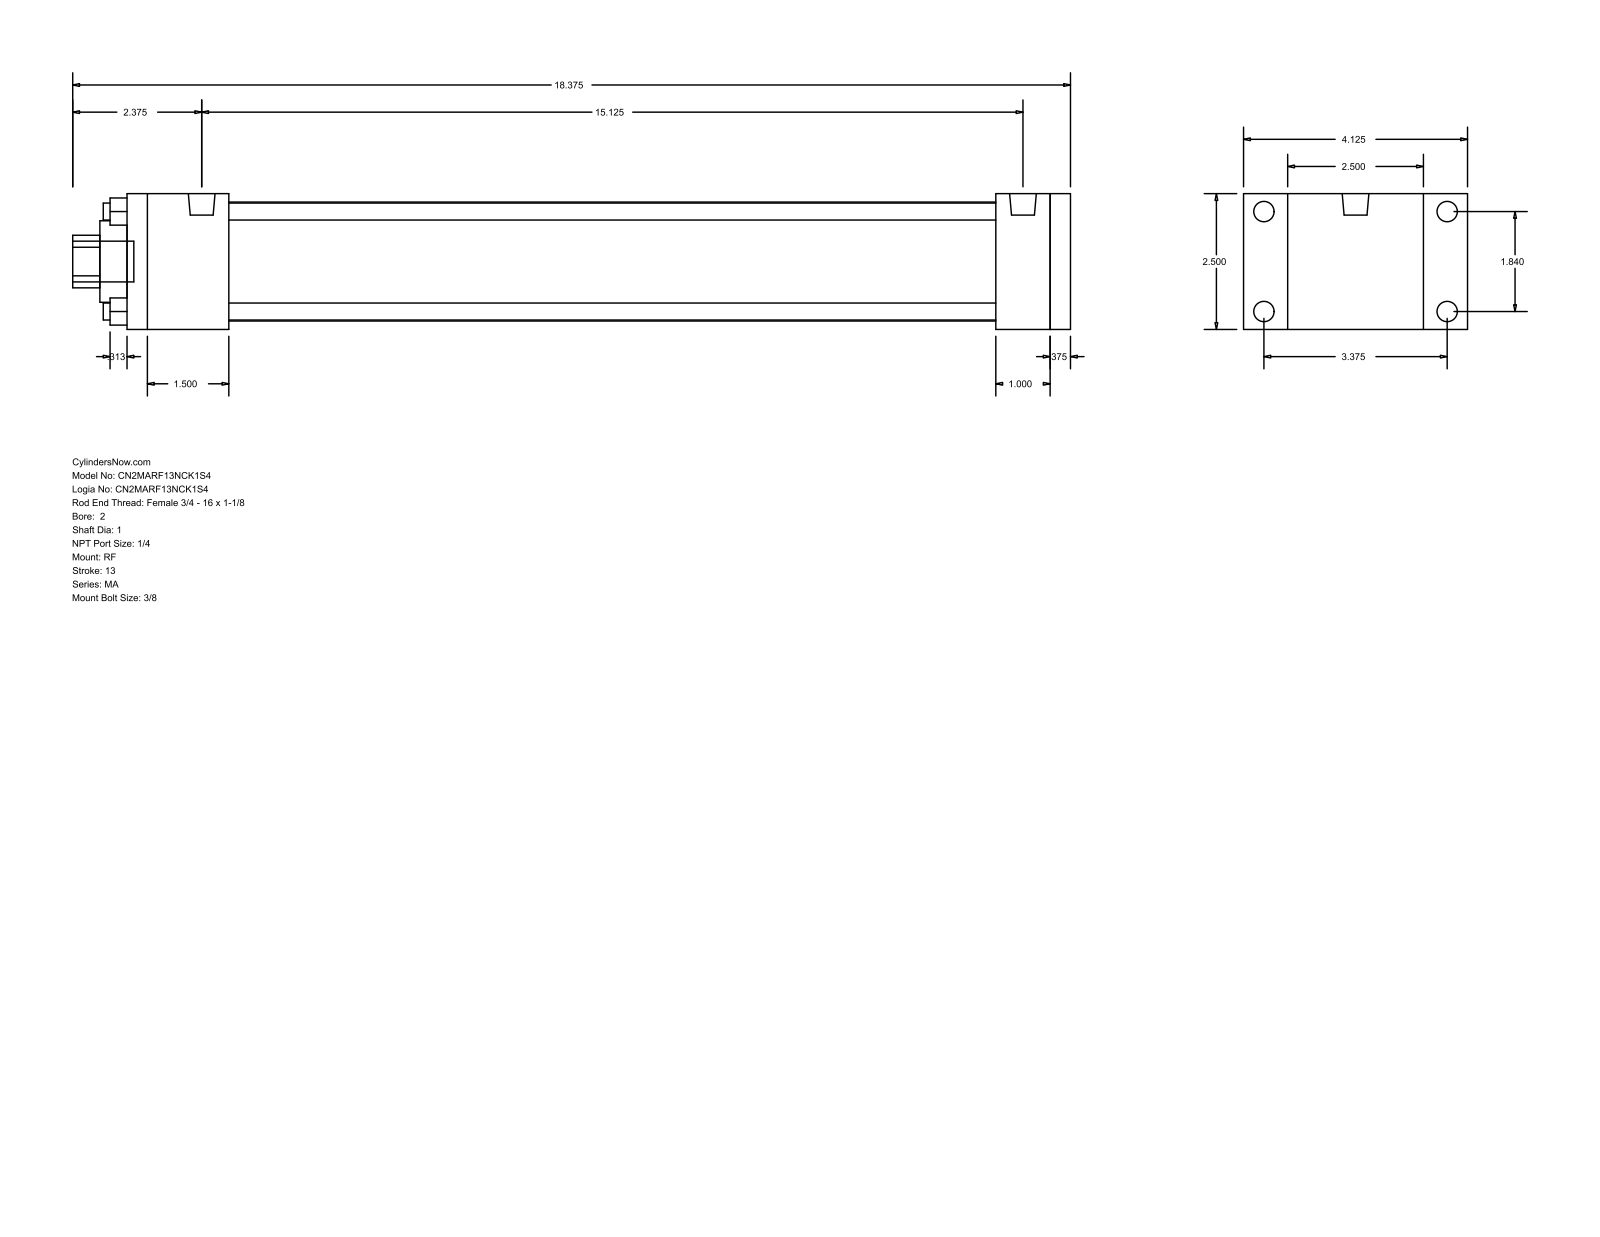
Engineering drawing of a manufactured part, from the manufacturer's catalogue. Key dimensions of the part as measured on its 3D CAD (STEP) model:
Part name (STEP PRODUCT): MA_RF__0200_1
STEP written by: GSSL Pune (CONFIG_CONTROL_DESIGN)
Units: millimetres
Bodies: 0 solids, 92 faces (64 planar, 28 cylindrical, 0 other)
Overall size (bounding box): 466.73 × 104.78 × 63.5
Round holes (diameter × count): ⌀7.94 ×4, ⌀25.4 ×1, ⌀38.1 ×1, ⌀55.63 ×1
Round bosses / shafts (diameter × count): ⌀9.53 ×4, ⌀7.94 ×4, ⌀12.49 ×2, ⌀19.05 ×1
Partial cylindrical surfaces — rounded edges, fillets, slot ends (radius × count): R12.29 ×1
Main face-to-face distances: 63.5, 431.8, 9.53, 441.33, 25.4, 20.64, 12.7, 47.63, 384.17, 393.7
Hole centre spacings: 33.05, 46.74, 66.1
